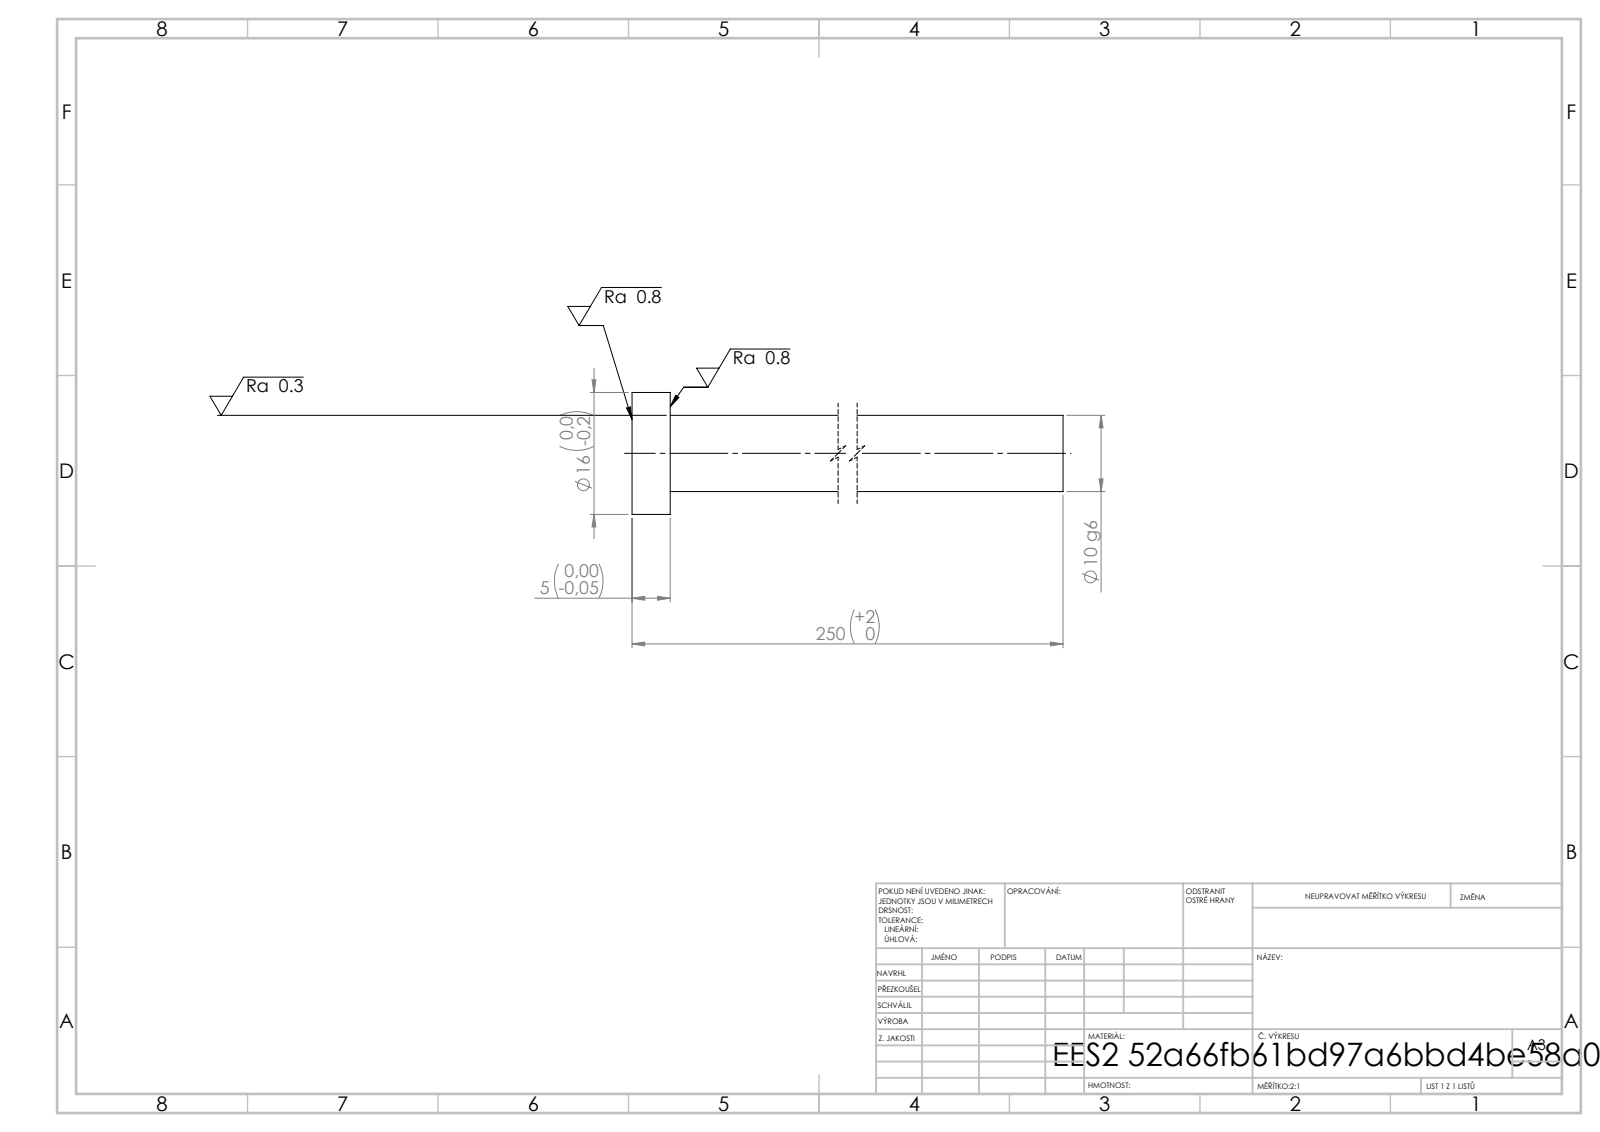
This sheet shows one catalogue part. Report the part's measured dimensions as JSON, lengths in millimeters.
{"step_written_by": "SolidWorks 2019 (CONFIG_CONTROL_DESIGN)", "units": "millimeters", "bodies": {"solids": 1, "faces": 7, "planar": 3, "cylindrical": 4, "other": 0}, "overall_size": [250, 16, 16], "volume_mm3": 20248, "surface_area_mm2": 8350, "round_bosses_or_shafts": [[16, 1], [10, 1]], "face_to_face_distances": [5, 250, 245]}
